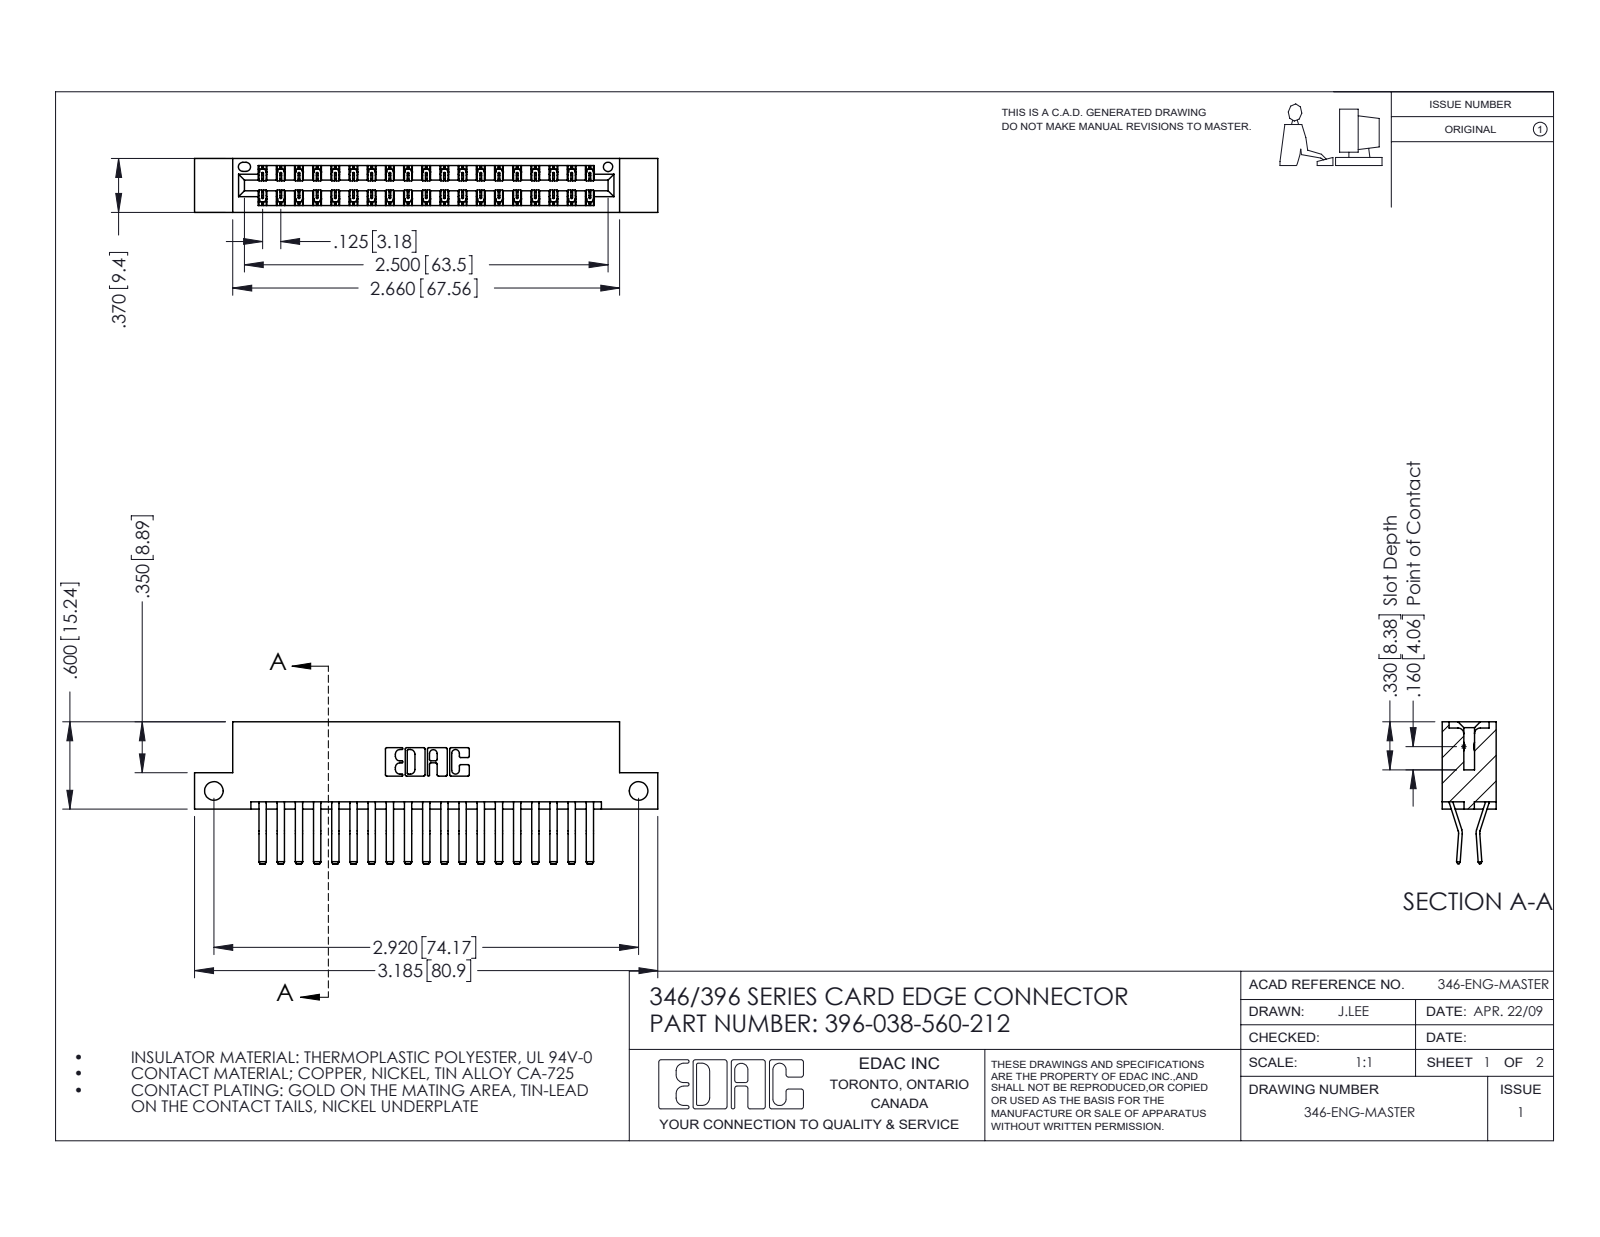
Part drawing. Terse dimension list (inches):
name: 396-038-560-212; 345-292-001_560 Tail; 346 Part_Flush Mounting Lugs - Side Mount
written by: SolidWorks 2016 (CONFIG_CONTROL_DESIGN)
unit: in
bodies: 39 solids, 2174 faces (1406 planar, 768 cylindrical, 0 other)
size: 3.185 × 0.975 × 0.37
volume: 0.48 in³; area: 17.03 in²
holes: 2× ⌀0.128, 1× ⌀0.064
rounds: 57× R0.006, 22× R0.01, 6× R0.007, 6× R0.031, 3× R0.026, 2× R0.01, 2× R0.014, 2× R0.022
face distances: 0.048, 0.322, 0.25, 0.37, 0.025, 0.072, 0.298, 0.275, 0.148, 0.222
hole spacings: 2.92
